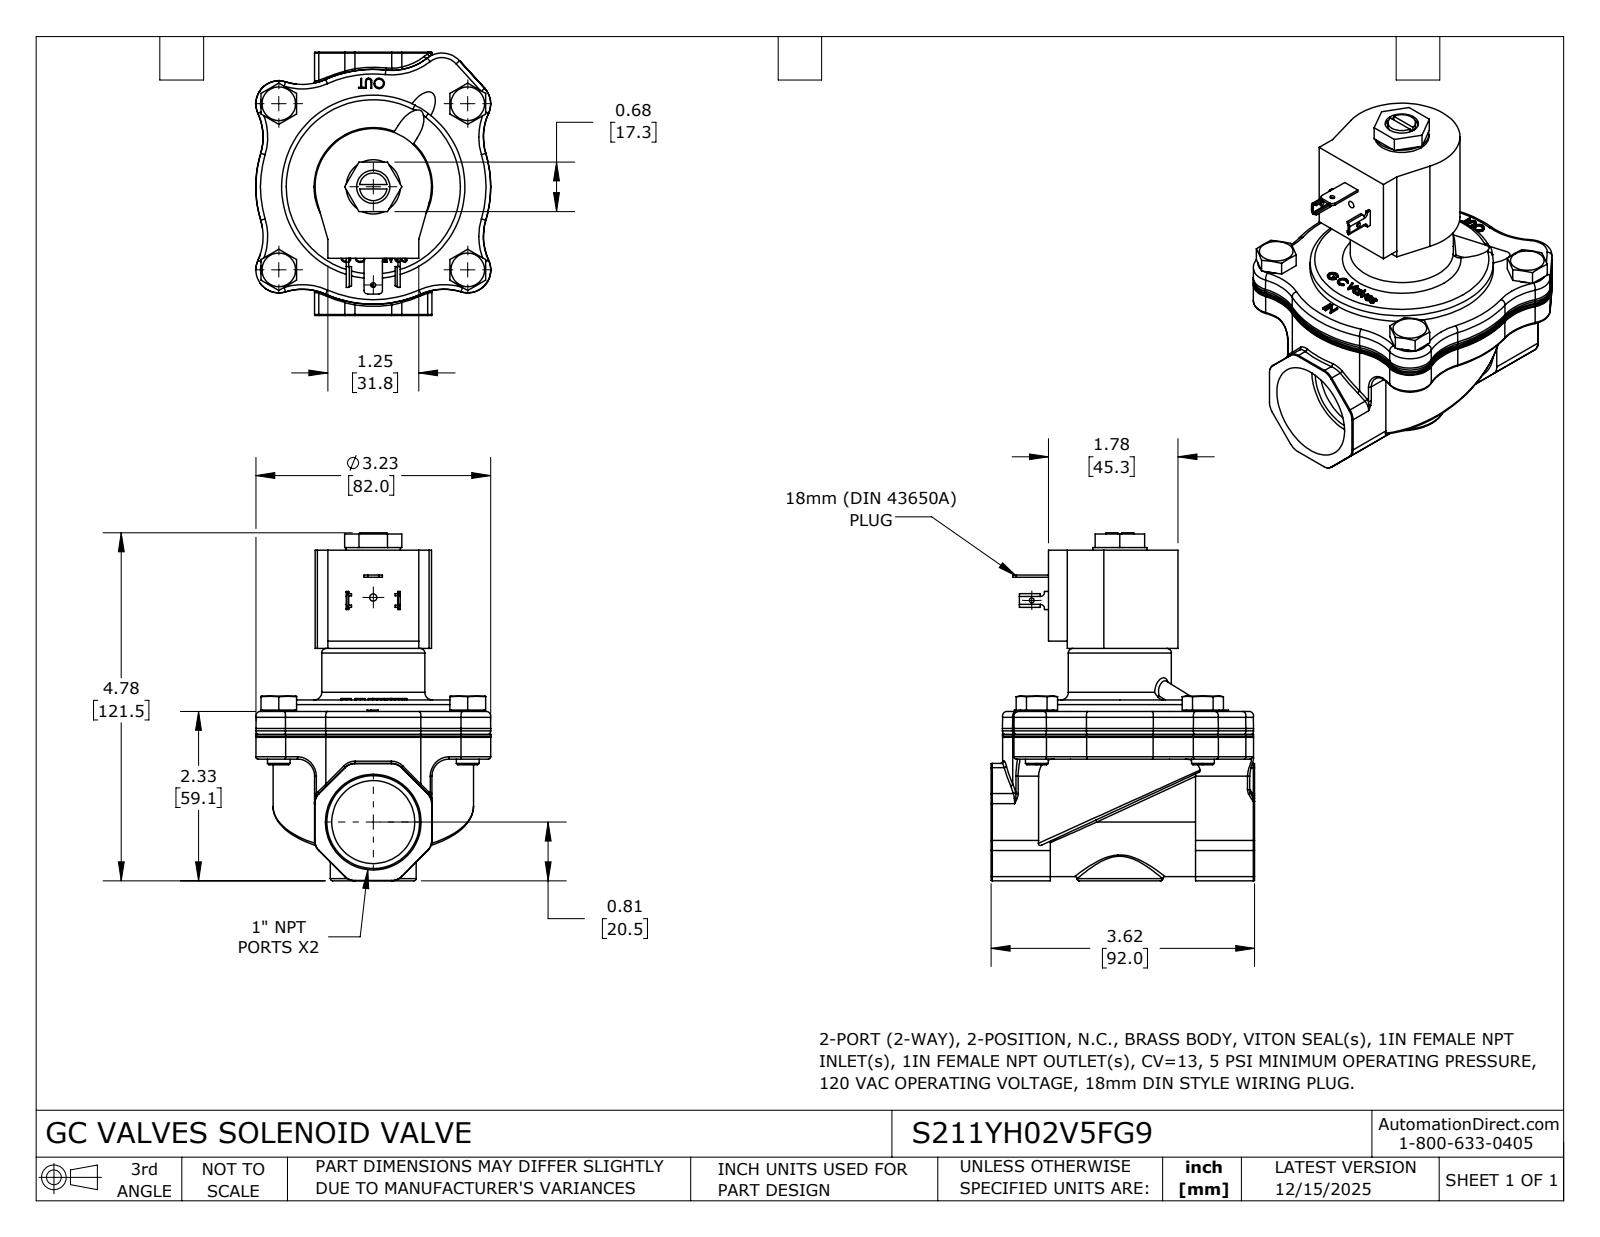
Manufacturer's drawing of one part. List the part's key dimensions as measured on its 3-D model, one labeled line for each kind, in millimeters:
Part name (STEP PRODUCT): S211YH02V5FG9
STEP written by: SolidWorks 2024 (CONFIG_CONTROL_DESIGN)
Units: millimetres
Bodies: 1 solid, 691 faces (224 planar, 180 cylindrical, 287 other)
Overall size (bounding box): 121.5 × 92 × 82.1
Volume: 314 800 mm³ · Surface area: 43 790 mm²
Round holes (diameter × count): ⌀1.7 ×1, ⌀1.7 ×1, ⌀2.5 ×1, ⌀11.6 ×1, ⌀29 ×1
Round bosses / shafts (diameter × count): ⌀11.4 ×4, ⌀8 ×4, ⌀64 ×1, ⌀36 ×1, ⌀30 ×1, ⌀18.9 ×1, ⌀9.7 ×1
Partial cylindrical surfaces — rounded edges, fillets, slot ends (radius × count): R0.8 ×24, R20 ×24, R8 ×12, R5 ×8, R0.2 ×4, R1 ×4, R1.3 ×2, R1.5 ×2
Main face-to-face distances: 4, 56.3, 52.3, 59.1, 63.1, 115.4, 42.5, 16.6, 20.6, 72.9
Hole centre spacings: 34.3, 78.4
